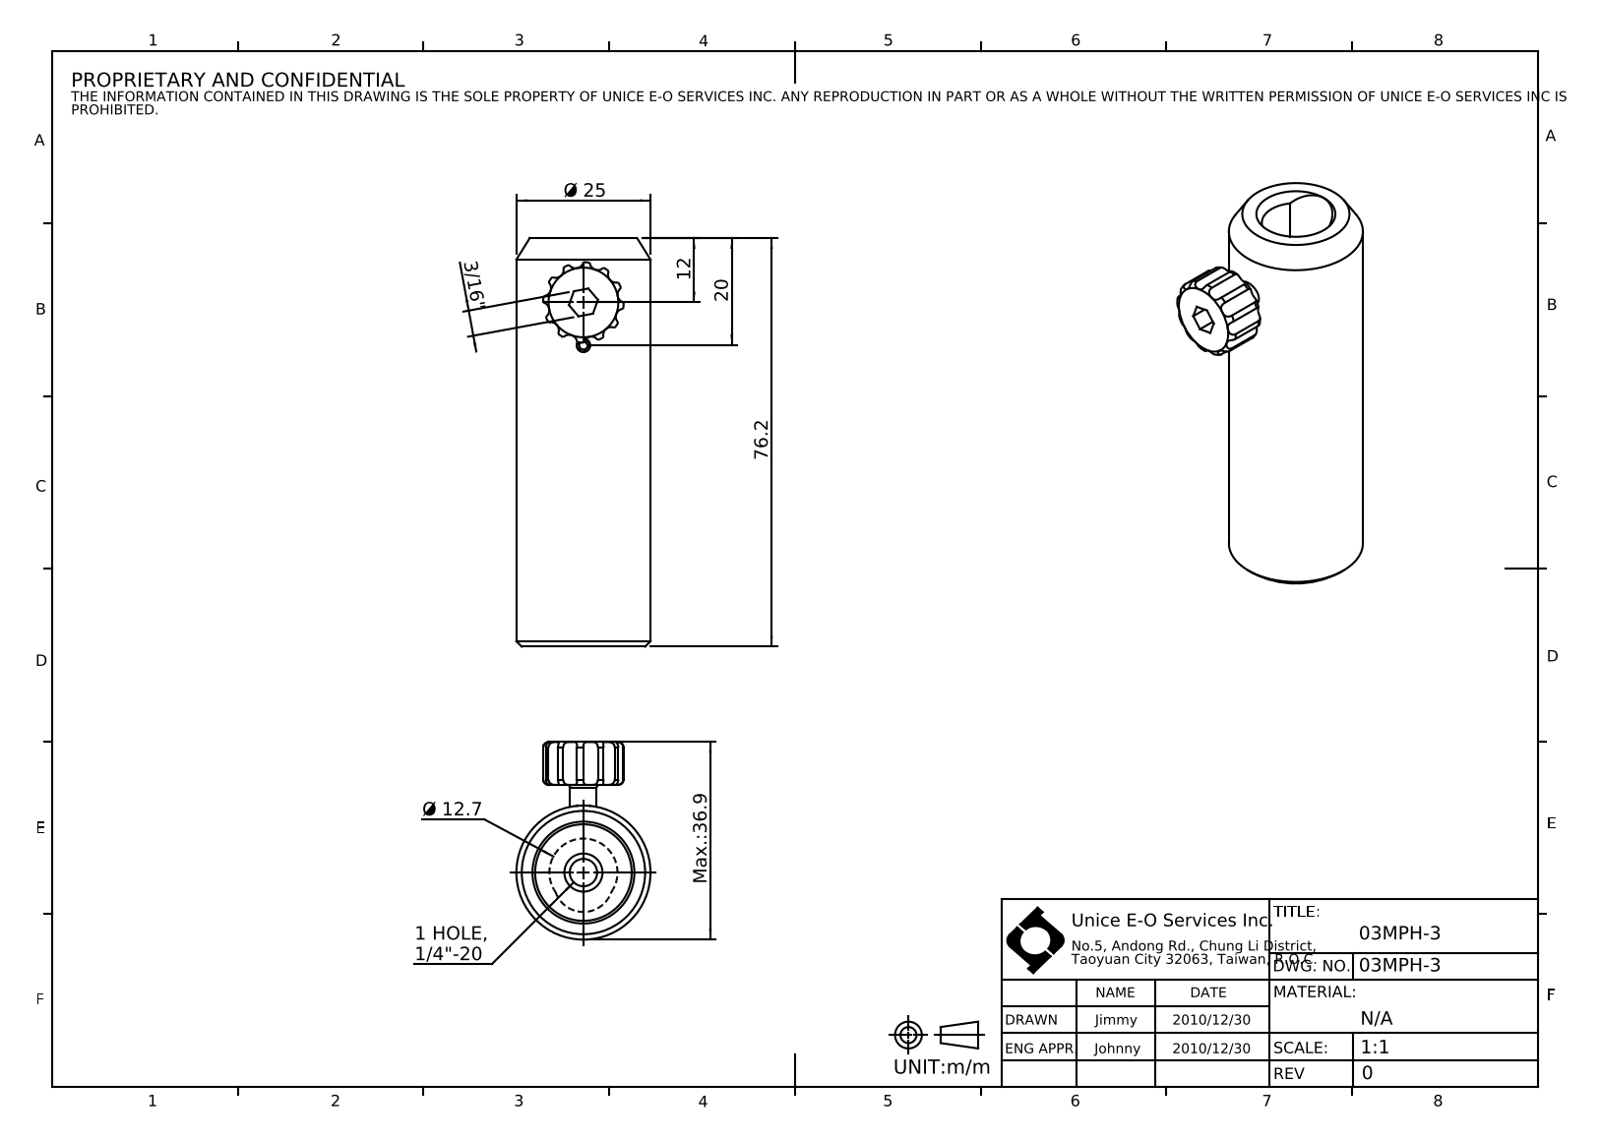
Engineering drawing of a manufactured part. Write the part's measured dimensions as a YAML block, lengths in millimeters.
part_name: "03MPH-3"
step_written_by: "SolidWorks 2016 (CONFIG_CONTROL_DESIGN)"
units: millimeters
bodies: {solids: 0, faces: 96, planar: 16, cylindrical: 42, other: 38}
overall_size: [76.2, 36.85, 25]
round_holes:
  - {diameter: 2.5, count: 1}
  - {diameter: 5.11, count: 1}
  - {diameter: 19, count: 1}
round_bosses_or_shafts:
  - {diameter: 25, count: 1}
  - {diameter: 4.94, count: 1}
partial_cylinders:
  - {radius: 1.5, count: 12}
  - {radius: 5.5, count: 1}
  - {radius: 6.35, count: 1}
  - {radius: 7.5, count: 1}
face_to_face_distances: [76.2, 8, 4.76, 4.75, 3.85, 11.85, 1.5]
